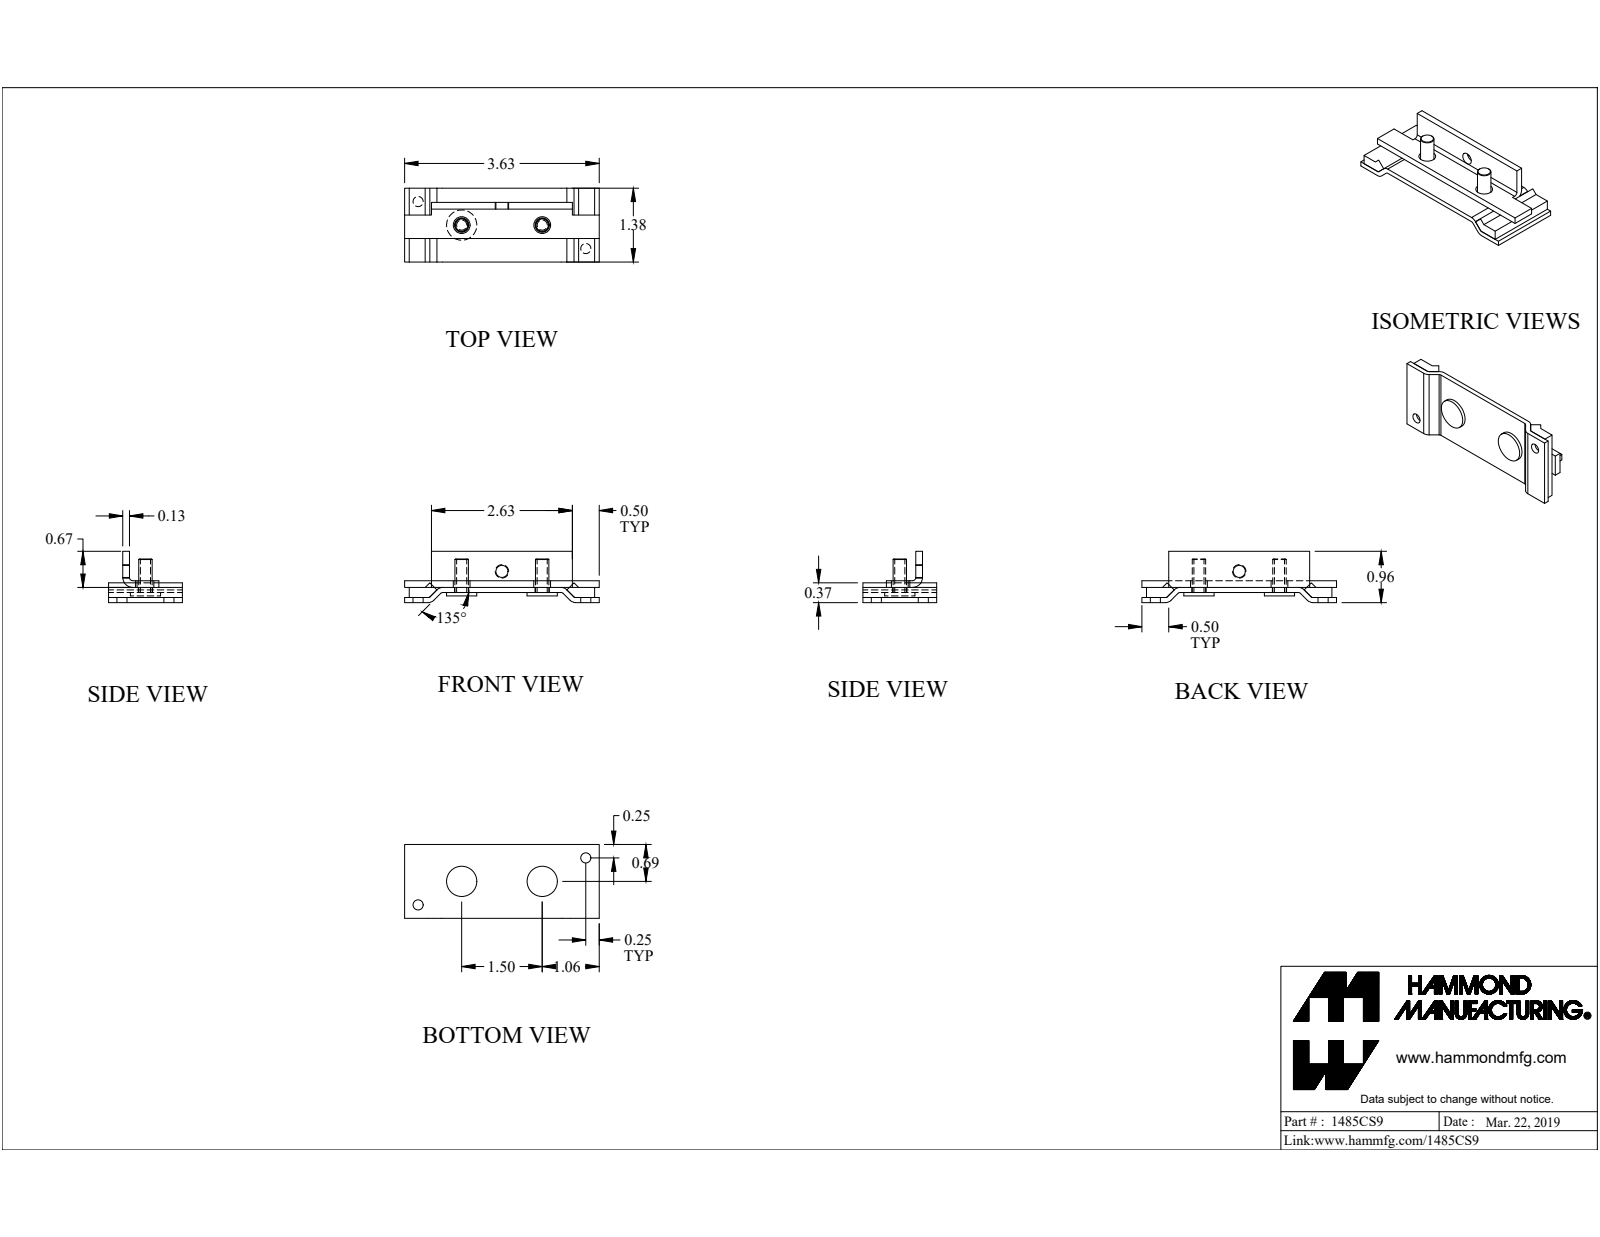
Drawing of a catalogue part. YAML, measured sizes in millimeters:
part_name: "1485CS9"
step_written_by: "SolidWorks 2019 (CONFIG_CONTROL_DESIGN)"
units: millimeters
bodies: {solids: 6, faces: 71, planar: 48, cylindrical: 21, other: 2}
overall_size: [92.1, 34.9, 24.3]
volume: 20300
surface_area: 16610
round_holes:
  - {diameter: 4.7, count: 2}
  - {diameter: 6.7, count: 2}
  - {diameter: 8, count: 2}
  - {diameter: 5.7, count: 1}
round_bosses_or_shafts:
  - {diameter: 14.3, count: 2}
  - {diameter: 6.4, count: 2}
partial_cylinders:
  - {radius: 1.2, count: 4}
  - {radius: 3.6, count: 4}
  - {radius: 1.5, count: 1}
  - {radius: 4.7, count: 1}
face_to_face_distances: [2.4, 3.2, 2.4, 4.8, 2.4, 7.2, 8, 5.6, 4.7, 10.3]
hole_center_spacings: [23.4, 59.8, 38.1, 82.4]
